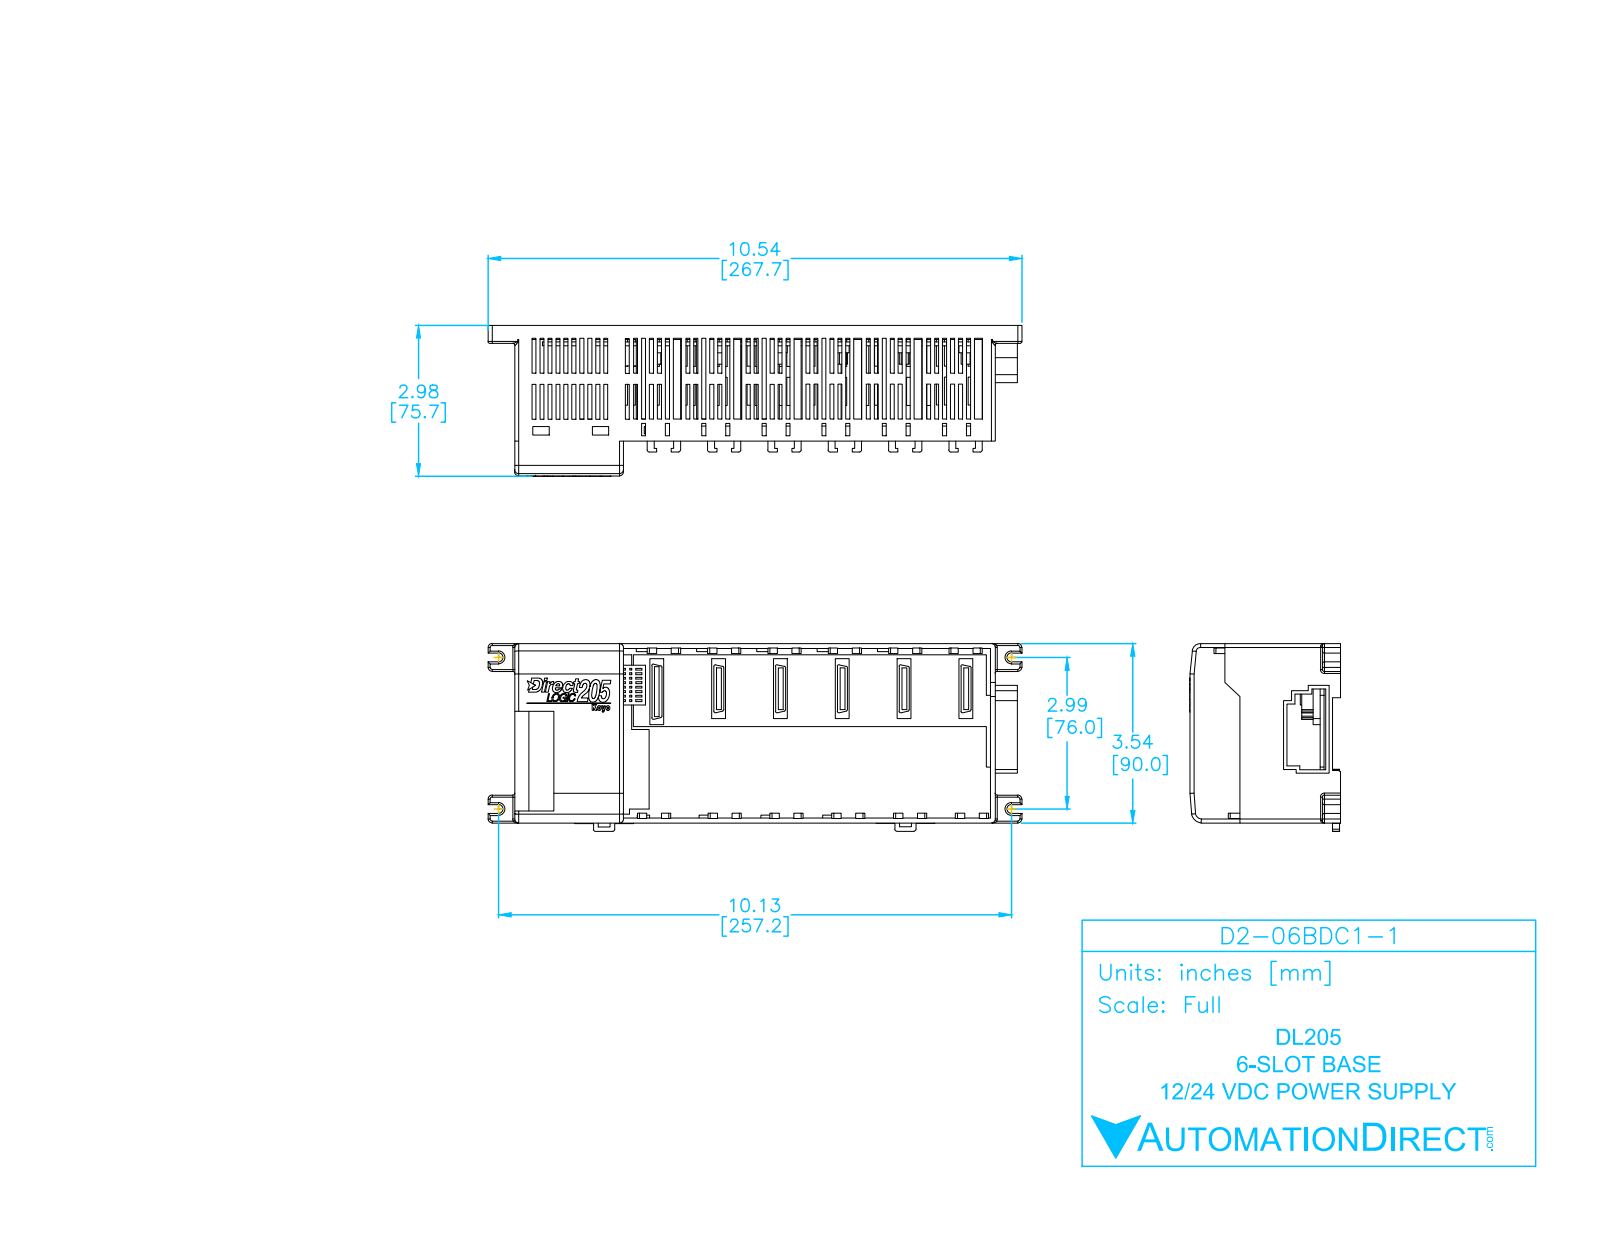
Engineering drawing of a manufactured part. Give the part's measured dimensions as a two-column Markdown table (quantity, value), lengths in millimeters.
| quantity | value |
| --- | --- |
| part name | D2-06BDC1-1 |
| STEP written by | SolidWorks 2009 (AUTOMOTIVE_DESIGN) |
| units | millimeters |
| bodies | 6 solids, 2240 faces (1903 planar, 174 cylindrical, 163 other) |
| overall size | 267.67 × 94.22 × 75.7 |
| volume | 289 596 mm³ |
| surface area | 191 595 mm² |
| round bosses / shafts (diameter × count) | 5.42 × 6 |
| partial cylindrical surfaces (radius × count) | 1 × 64, 0.75 × 24, 2 × 20, 0.25 × 16, 2.21 × 4, 4.71 × 4, 4.12 × 1, 5.29 × 1 |
| main face-to-face distances | 2.5, 3, 1.25, 85, 87.5, 2, 4.25, 6.25, 3.25, 90 |
